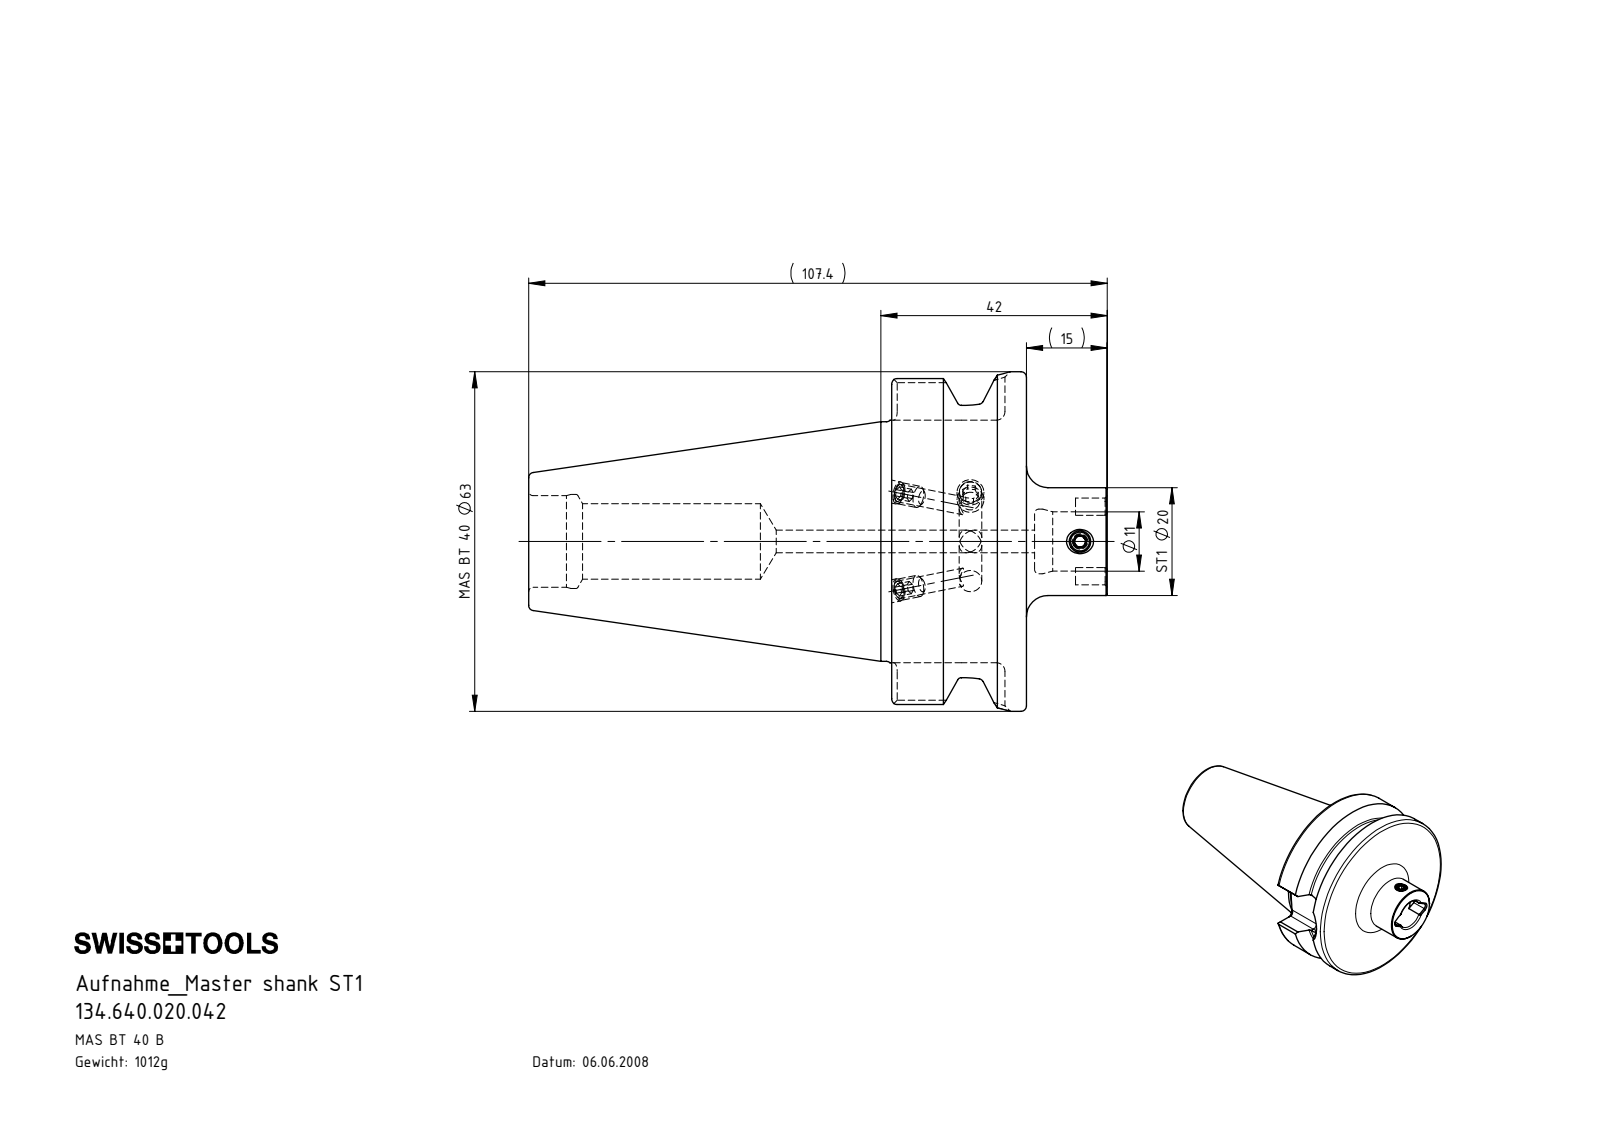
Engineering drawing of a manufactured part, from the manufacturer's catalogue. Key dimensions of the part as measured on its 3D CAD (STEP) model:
Part name (STEP PRODUCT): ST1-ER1.001.005_A; BB4-ST1.K01.042; BB4-ST1.K01.042_A_mit Bundkhlung; ISO 4026 - M5 x 5_PreviewCfg
STEP written by: SolidWorks 2015 (CONFIG_CONTROL_DESIGN)
Units: millimetres
Bodies: 3 solids, 172 faces (45 planar, 57 cylindrical, 70 other)
Overall size (bounding box): 107.4 × 63 × 63
Volume: 128 678 mm³ · Surface area: 23 364 mm²
Round holes (diameter × count): ⌀4 ×2, ⌀4.2 ×2, ⌀3.5 ×1, ⌀11 ×1, ⌀12 ×1, ⌀14 ×1, ⌀17 ×1, ⌀17.45 ×1
Round bosses / shafts (diameter × count): ⌀63 ×1, ⌀53 ×1, ⌀44.45 ×1, ⌀20 ×1, ⌀5 ×1, ⌀4 ×1
Partial cylindrical surfaces — rounded edges, fillets, slot ends (radius × count): R1.6 ×8, R1.3 ×2, R8.05 ×1
Main face-to-face distances: 25, 45, 67.4, 92.4, 107.4, 40, 15, 16.1, 93.9, 26.5
